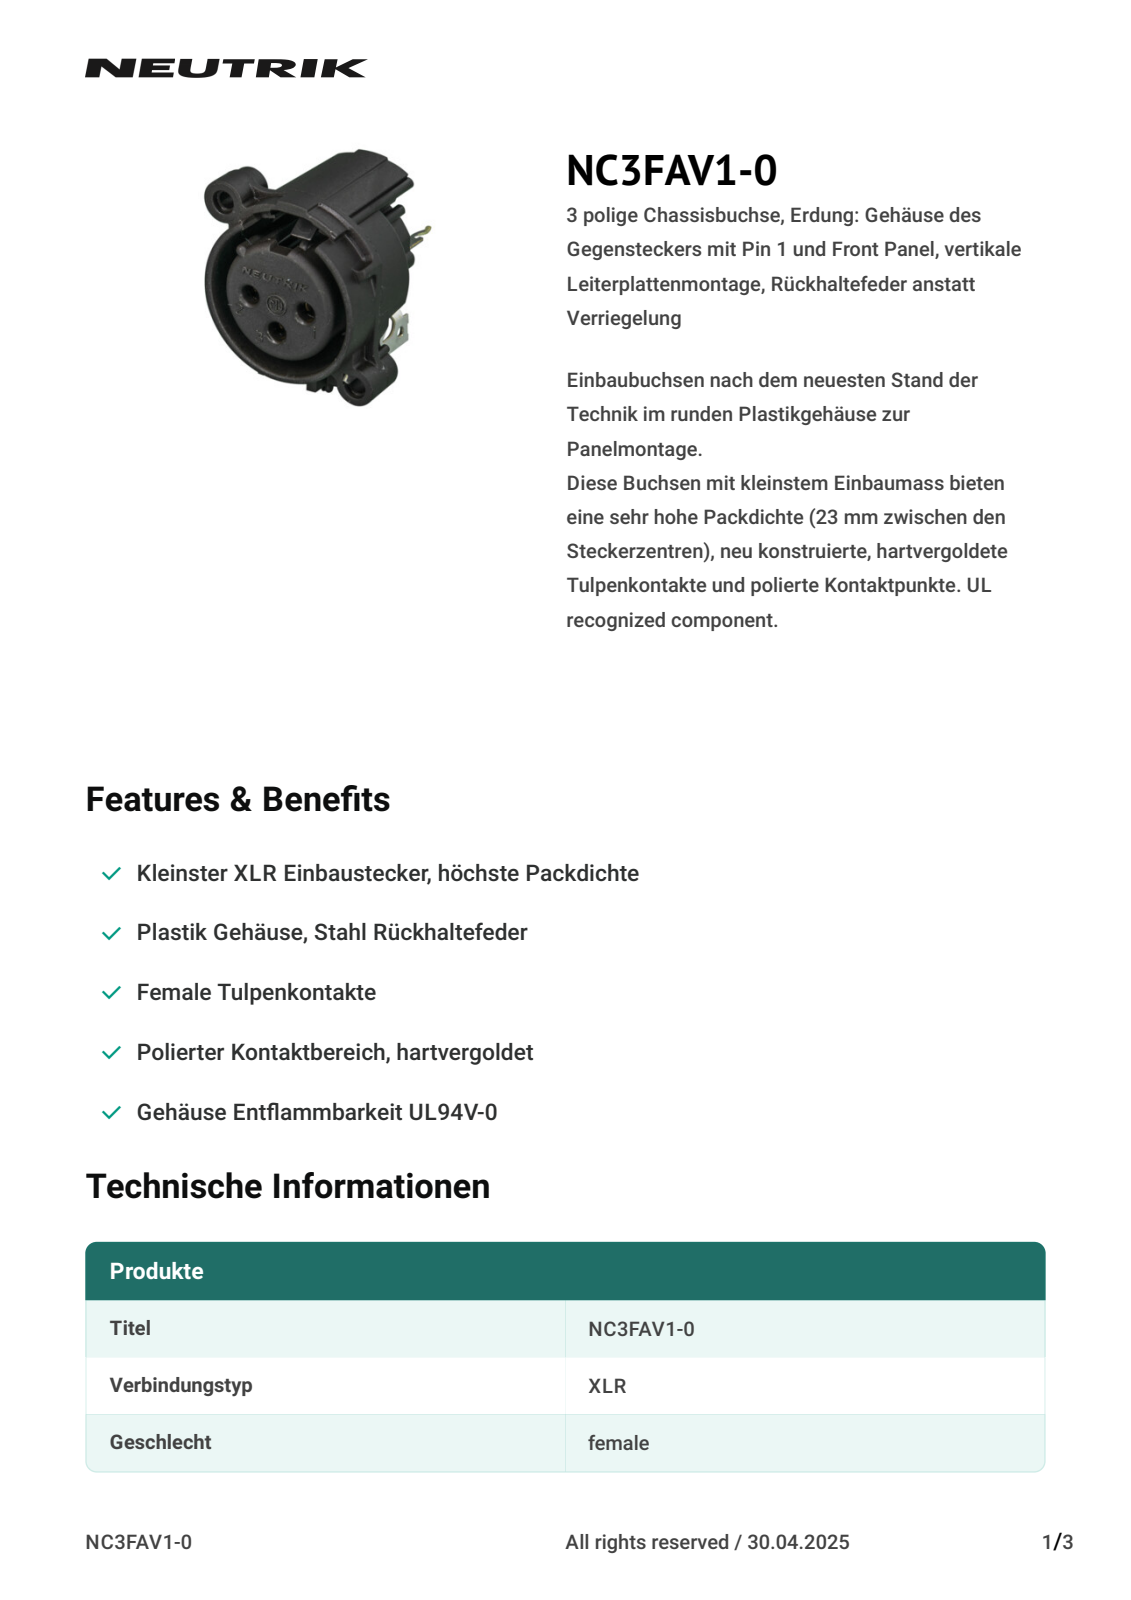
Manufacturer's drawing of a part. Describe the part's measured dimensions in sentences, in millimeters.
The part is named "NC3FAV1-0". Its 3-D file was written by "CREO PARAMETRIC BY PTC INC, 2019080 (CONFIG_CONTROL_DESIGN)". It is 1 solid with 1312 faces: 688 planar, 311 cylindrical and 313 other. Overall it measures 31.11 by 26.8 by 25.3 millimeters. Its volume is 5 808 cubic millimeters and its surface area 5 214 square millimeters. Round holes: 4 of diameter 2.5, 2 of diameter 1.5, 2 of diameter 2.35, 2 of diameter 3, 1 of diameter 19.5, 1 of diameter 21.8. Round bosses or shafts: 3 of diameter 1.5, 1 of diameter 15.8, 1 of diameter 5.8, 1 of diameter 3. Partial cylindrical surfaces (rounded edges, fillets, slot ends): 120 of radius 0.2, 29 of radius 0.15, 16 of radius 1, 14 of radius 0.5, 9 of radius 0.12, 7 of radius 0.4, 7 of radius 0.75, 5 of radius 0.6. The main face-to-face distances are 0.5, 1.5, 10.3, 13, 20.22, 8.8, 5.72, 3.95, 14.5, 7.22. The hole center spacings are 4.05, 5.66, 11.5, 14, 17.11, 3.95, 8.1, 8.5.
